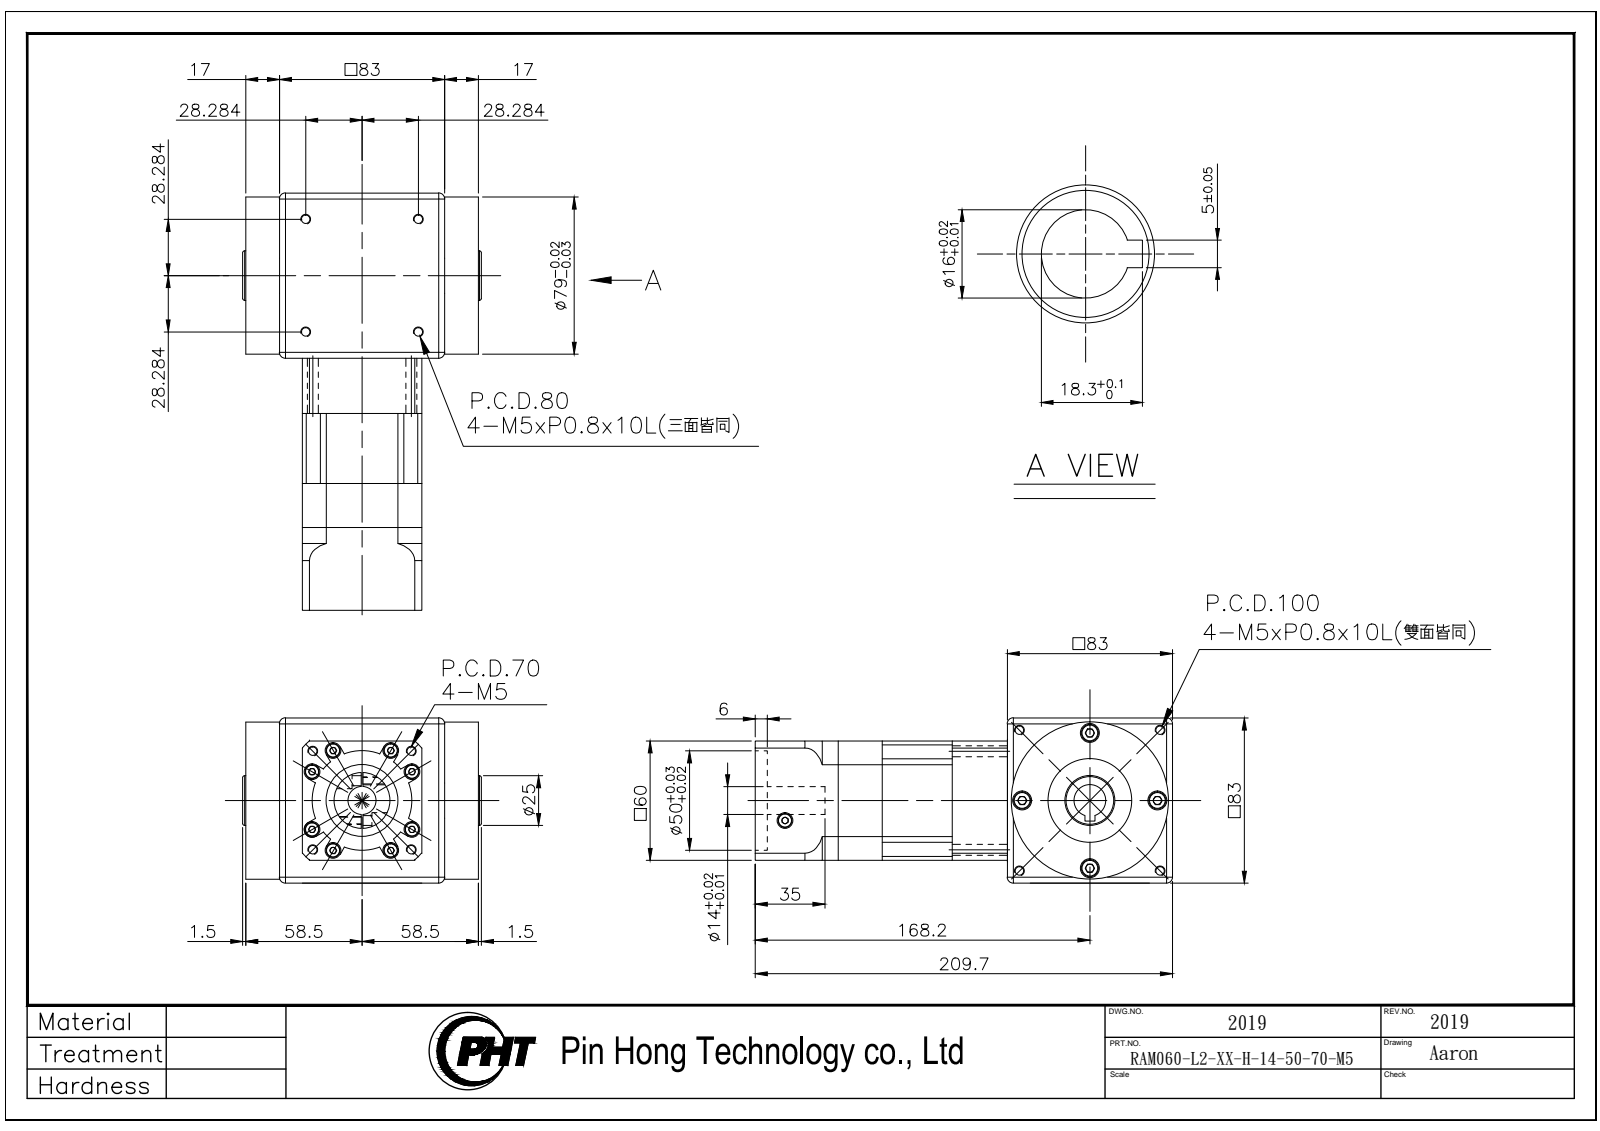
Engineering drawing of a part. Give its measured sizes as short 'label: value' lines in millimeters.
name: RAM060-L2-XX-H-14-50-70-M5_2019
written by: SolidWorks 2016 (AUTOMOTIVE_DESIGN)
unit: mm
bodies: 5 solids, 682 faces (324 planar, 235 cylindrical, 123 other)
size: 209.7 × 120 × 83
volume: 1 096 000 mm³; area: 139 128 mm²
holes: 16× ⌀4.2, 10× ⌀8, 8× ⌀4.5, 8× ⌀5.5, 4× ⌀9.5, 1× ⌀14, 1× ⌀16, 1× ⌀16.6, 1× ⌀36
bosses: 8× ⌀8.5, 8× ⌀7, 1× ⌀79, 1× ⌀55, 1× ⌀42, 1× ⌀28, 1× ⌀25
rounds: 4× R5, 1× R25, 1× R35, 1× R40, 1× R57.15
face distances: 71.5, 11.5, 83, 60, 27.7, 57.35, 85.05, 22.15, 35.2, 62.9
hole spacings: 29, 10.26, 14.14, 39.25, 41.01, 42.9, 50.9, 53.15
